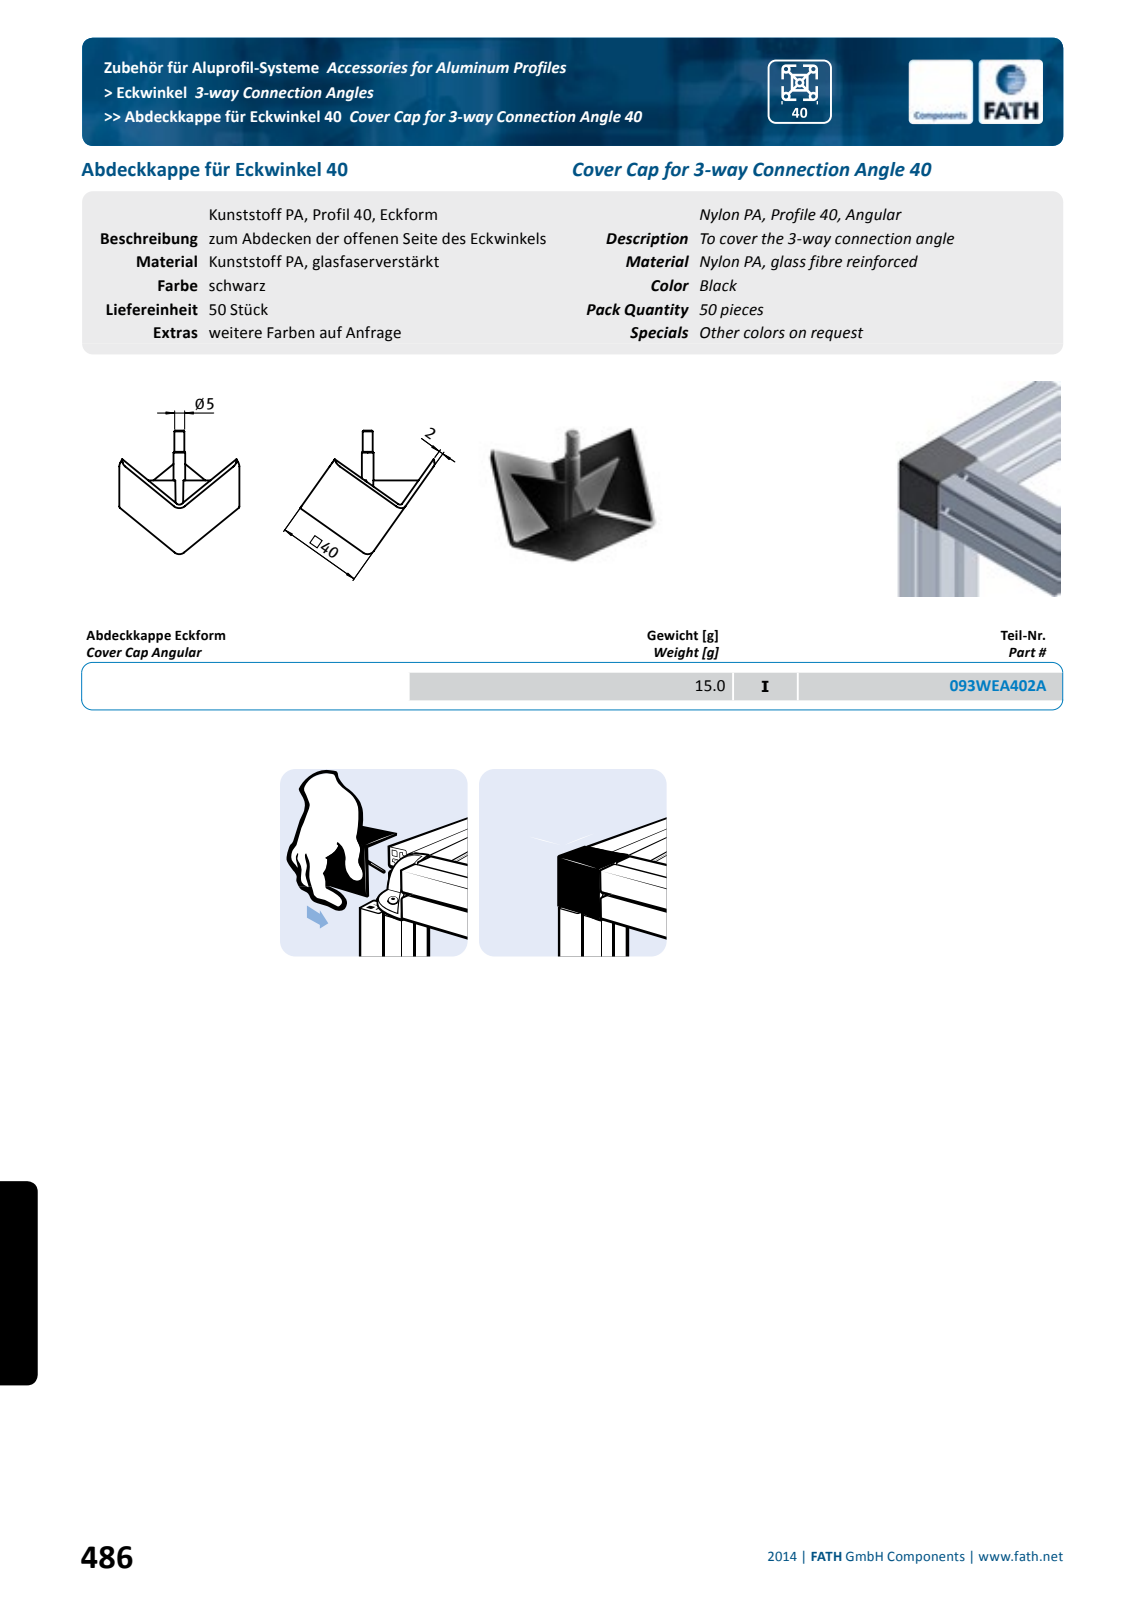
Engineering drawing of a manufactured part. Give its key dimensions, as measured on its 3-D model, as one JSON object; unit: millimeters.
{"part_name": "fath_093wea402a", "step_written_by": "Spatial InterOp 3D (automotive_design)", "units": "millimeters", "bodies": {"solids": 1, "faces": 82, "planar": 26, "cylindrical": 30, "other": 26}, "overall_size": [40, 40, 40], "volume_mm3": 11876, "surface_area_mm2": 11792, "round_bosses_or_shafts": [[5.4, 1], [5, 1]], "partial_cylinders_radius": [[0.3, 15], [1.5, 3], [2.5, 3], [3.5, 3]], "face_to_face_distances": [2, 40, 38, 23.69, 39, 37, 1]}
